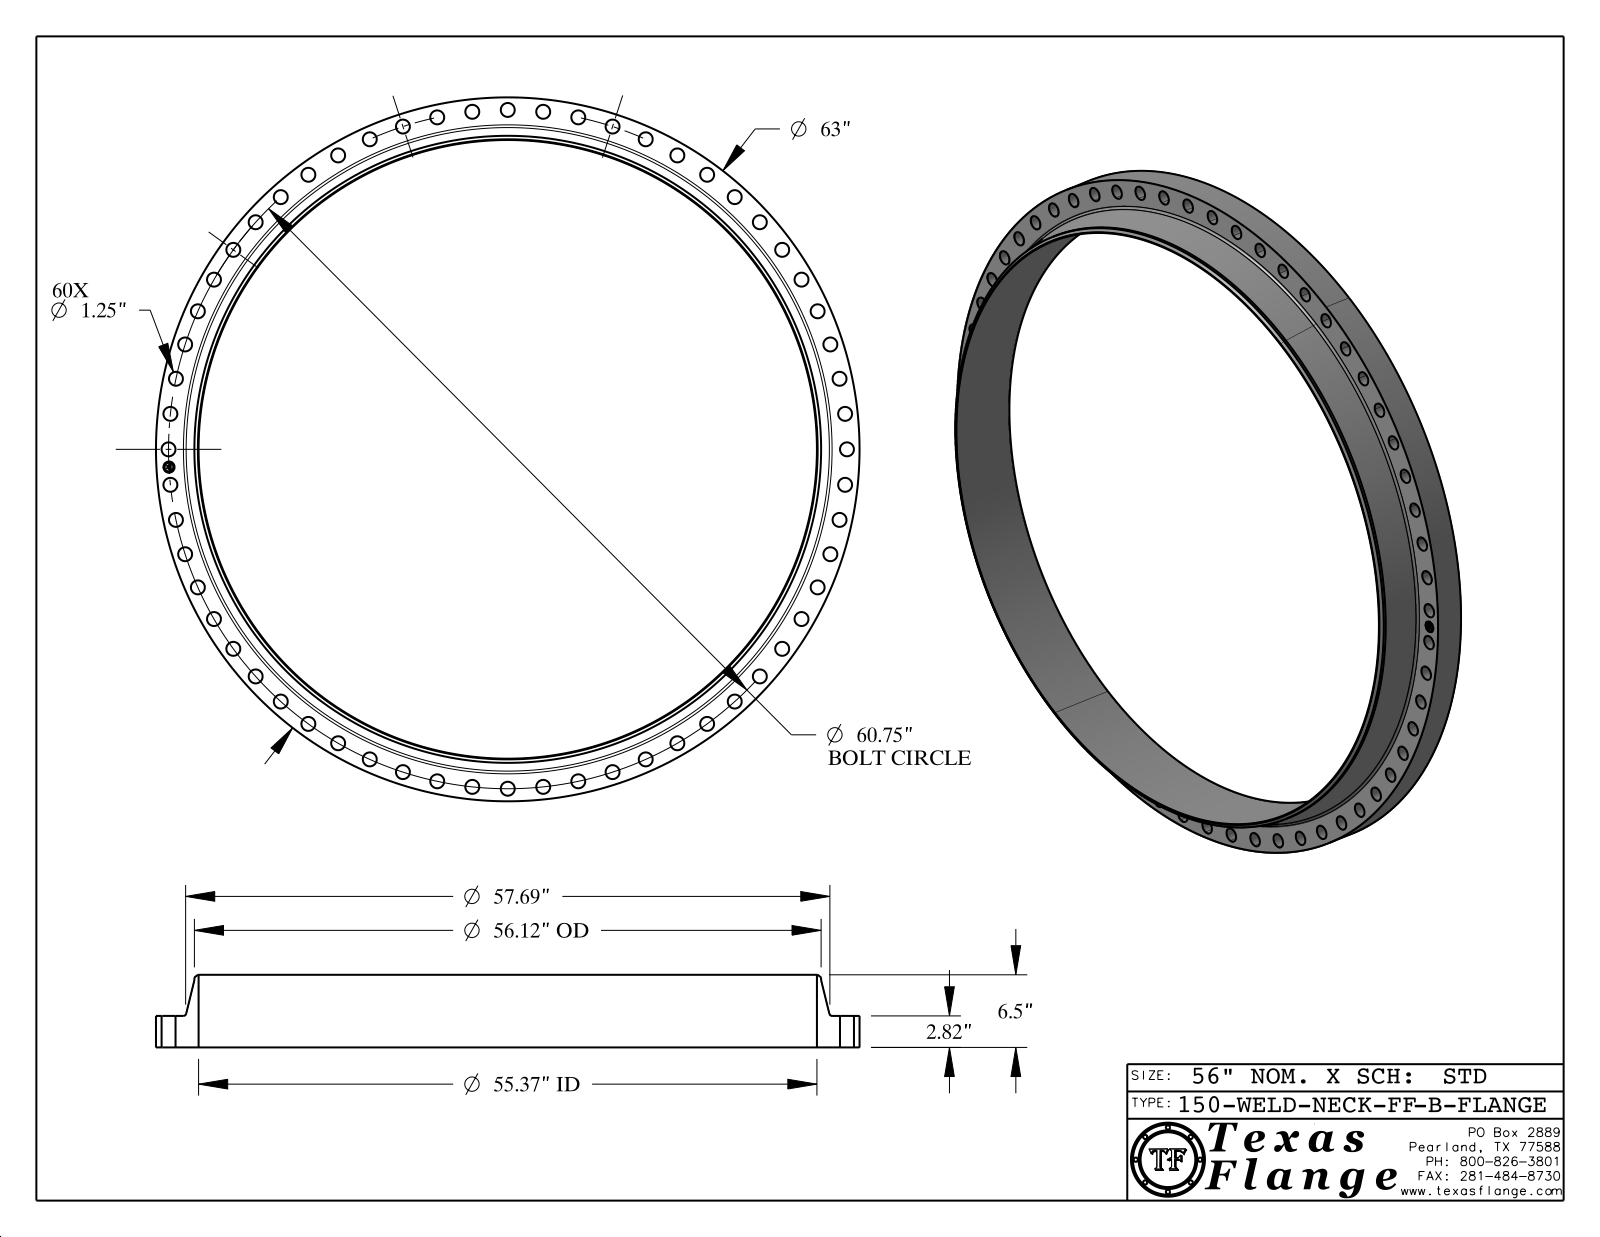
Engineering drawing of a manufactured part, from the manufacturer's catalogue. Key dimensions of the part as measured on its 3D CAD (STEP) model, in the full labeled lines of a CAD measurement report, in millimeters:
Part name (STEP PRODUCT): 150-WELD-NECK-FF, Series B
STEP written by: CATIA V5 STEP AP214 (AUTOMOTIVE_DESIGN)
Units: millimetres
Bodies: 1 solid, 520 faces (368 planar, 146 cylindrical, 6 other)
Overall size (bounding box): 1600.2 × 1600.2 × 165.1
Volume: 36 920 000 mm³ · Surface area: 2 657 000 mm²
Round holes (diameter × count): ⌀31.8 ×60, ⌀25.4 ×1, ⌀1406.4 ×1
Round bosses / shafts (diameter × count): ⌀1.5 ×8, ⌀1600.2 ×1, ⌀1425.4 ×1, ⌀20 ×1
Main face-to-face distances: 71.6, 165.1, 93.5, 71.2, 0.4, 93.9, 0.5, 7.6, 7.4, 1.4
Hole centre spacings: 399.4, 771.5, 771.5, 161.3, 476.8, 1524.1, 1534.6, 241.4
